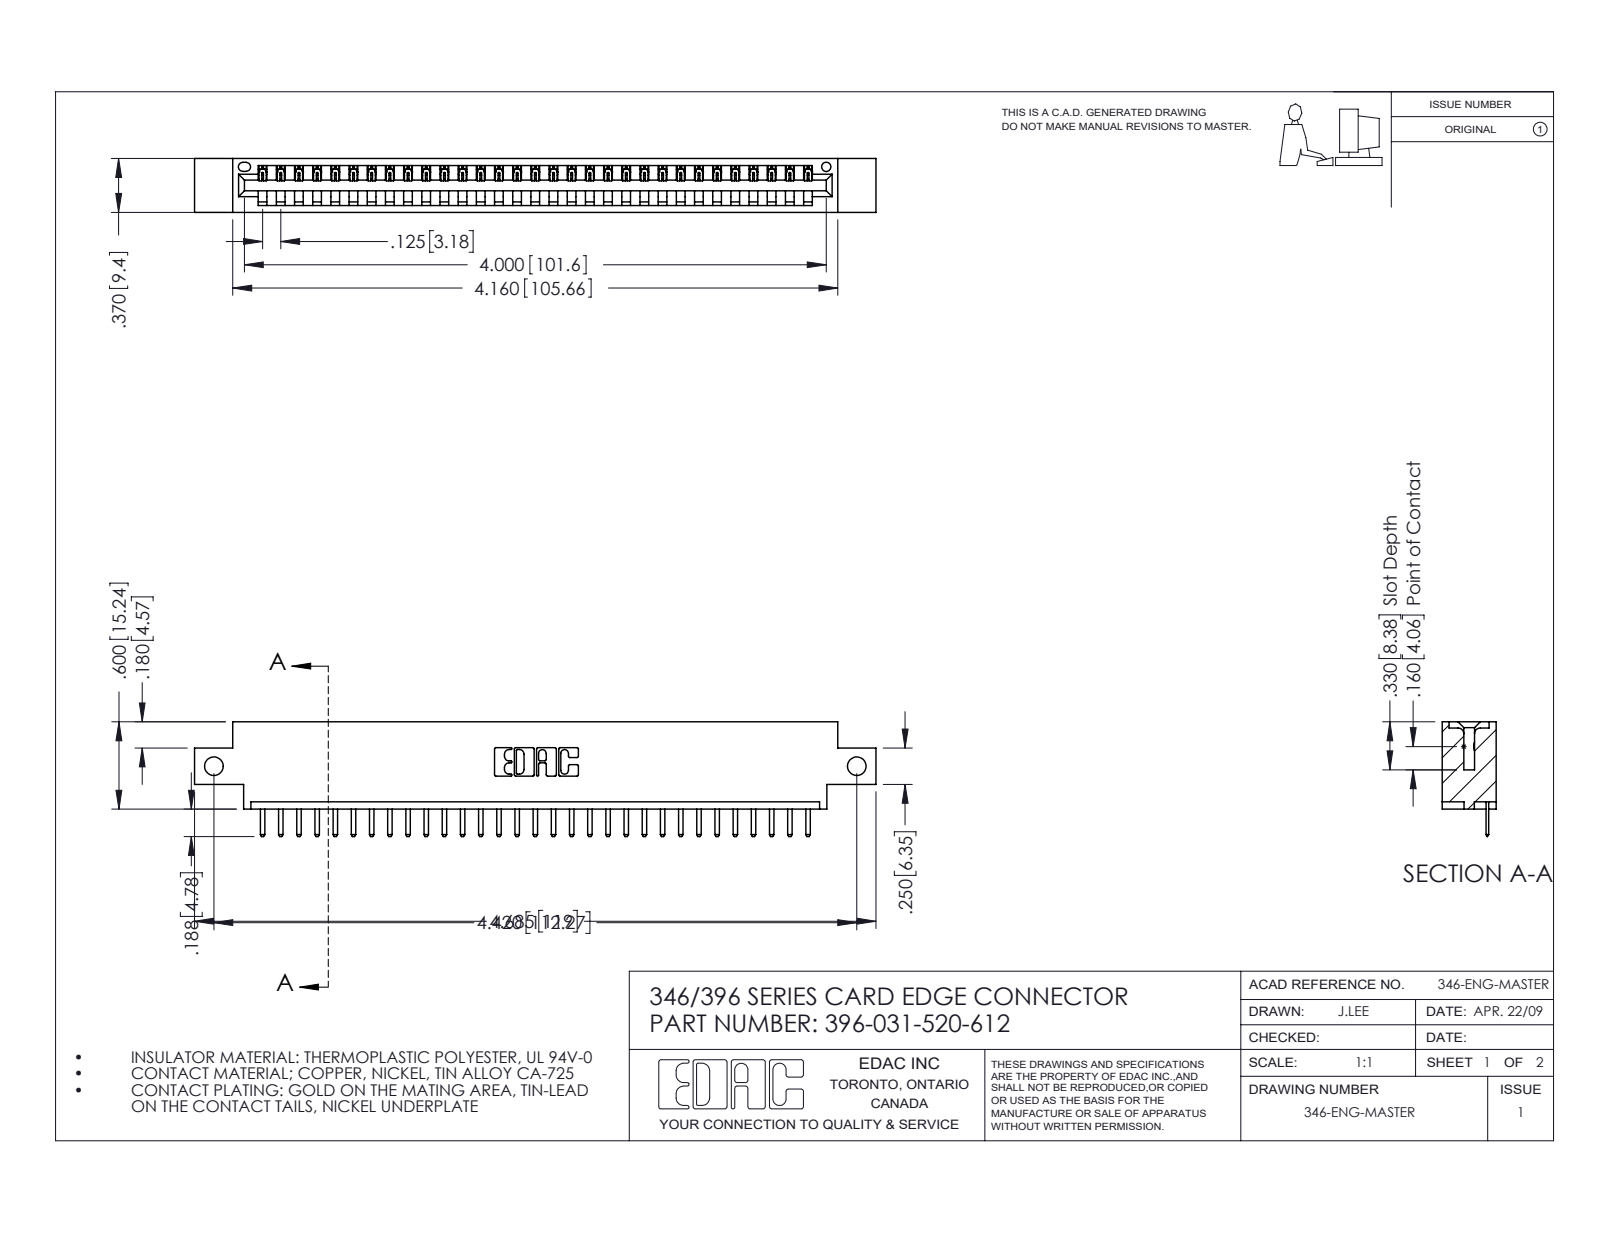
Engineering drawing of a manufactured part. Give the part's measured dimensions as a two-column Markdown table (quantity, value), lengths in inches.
| quantity | value |
| --- | --- |
| part name | 346 Part_0.170 Offset - Side Mount; 396-031-520-612; 345-292-001_345-293-120 |
| STEP written by | SolidWorks 2016 (CONFIG_CONTROL_DESIGN) |
| units | inches |
| bodies | 32 solids, 2048 faces (1382 planar, 666 cylindrical, 0 other) |
| overall size | 4.685 × 0.788 × 0.37 |
| volume | 0.67 in³ |
| surface area | 20.66 in² |
| round holes (diameter × count) | 0.128 × 2, 0.064 × 1 |
| partial cylindrical surfaces (radius × count) | 0.01 × 64, 0.006 × 62, 0.01 × 22, 0.007 × 6, 0.031 × 6, 0.026 × 3, 0.031 × 2, 0.04 × 2 |
| main face-to-face distances | 0.048, 0.322, 0.37, 0.25, 0.148, 0.222, 0.1, 0.174, 0.072, 0.298 |
| hole center spacings | 4.42 |
